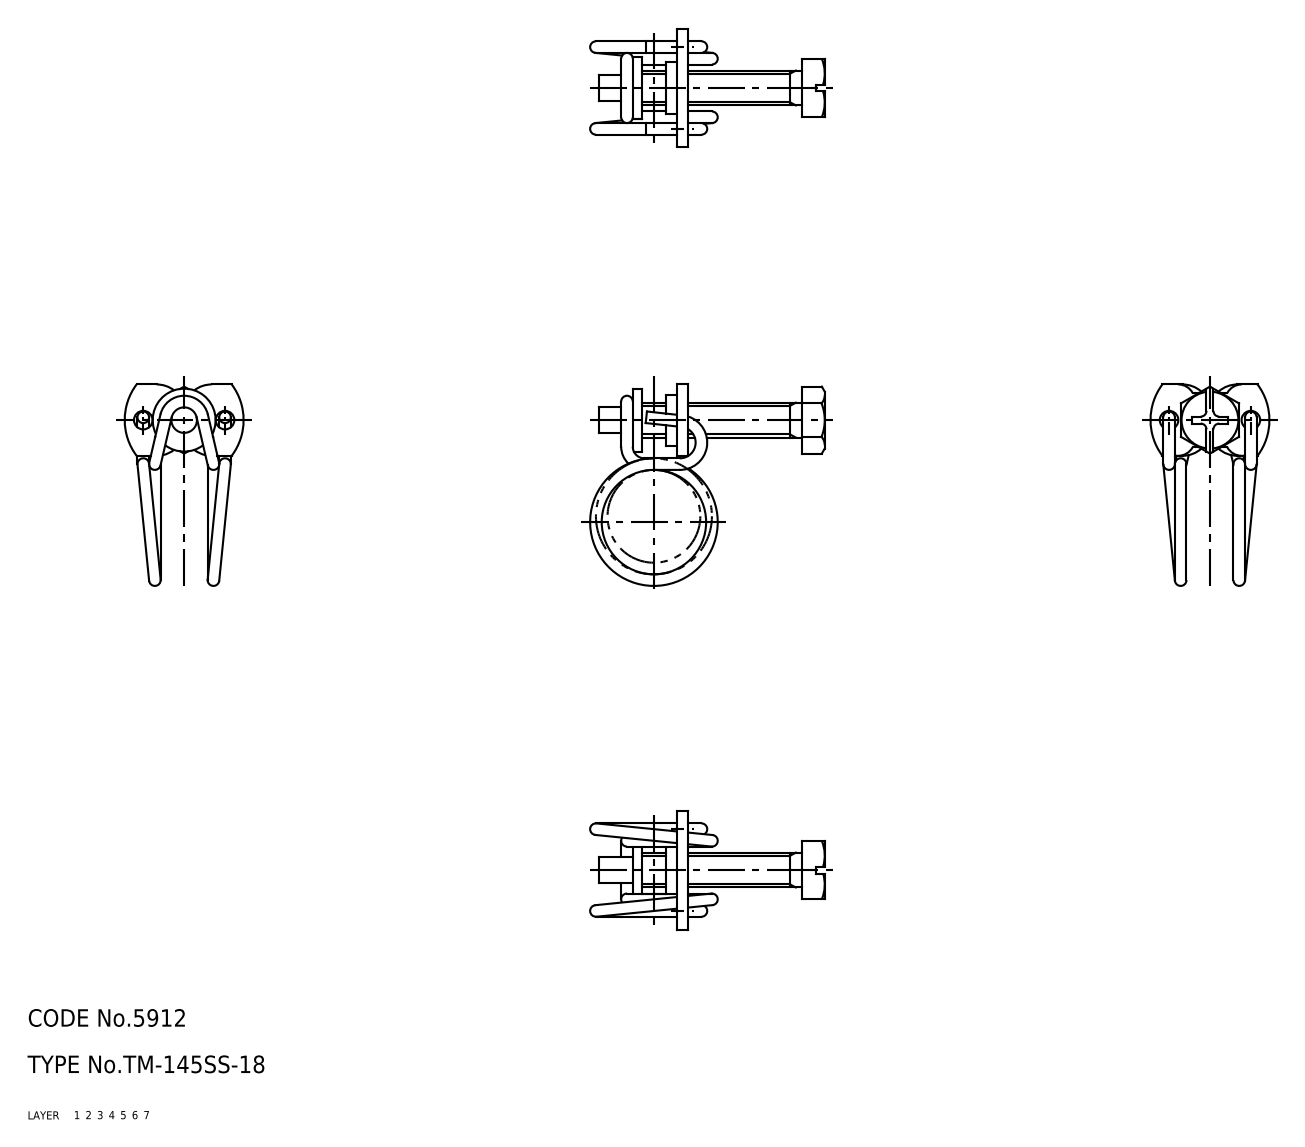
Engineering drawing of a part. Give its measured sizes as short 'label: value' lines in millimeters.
name: 67116437; 67116450; 67116463
written by: CADfix (AUTOMOTIVE_DESIGN)
unit: mm
bodies: 3 solids, 98 faces (0 planar, 0 cylindrical, 98 other)
size: 40.45 × 34.74 × 20.5
volume: 2 384 mm³; area: 3 053 mm²
